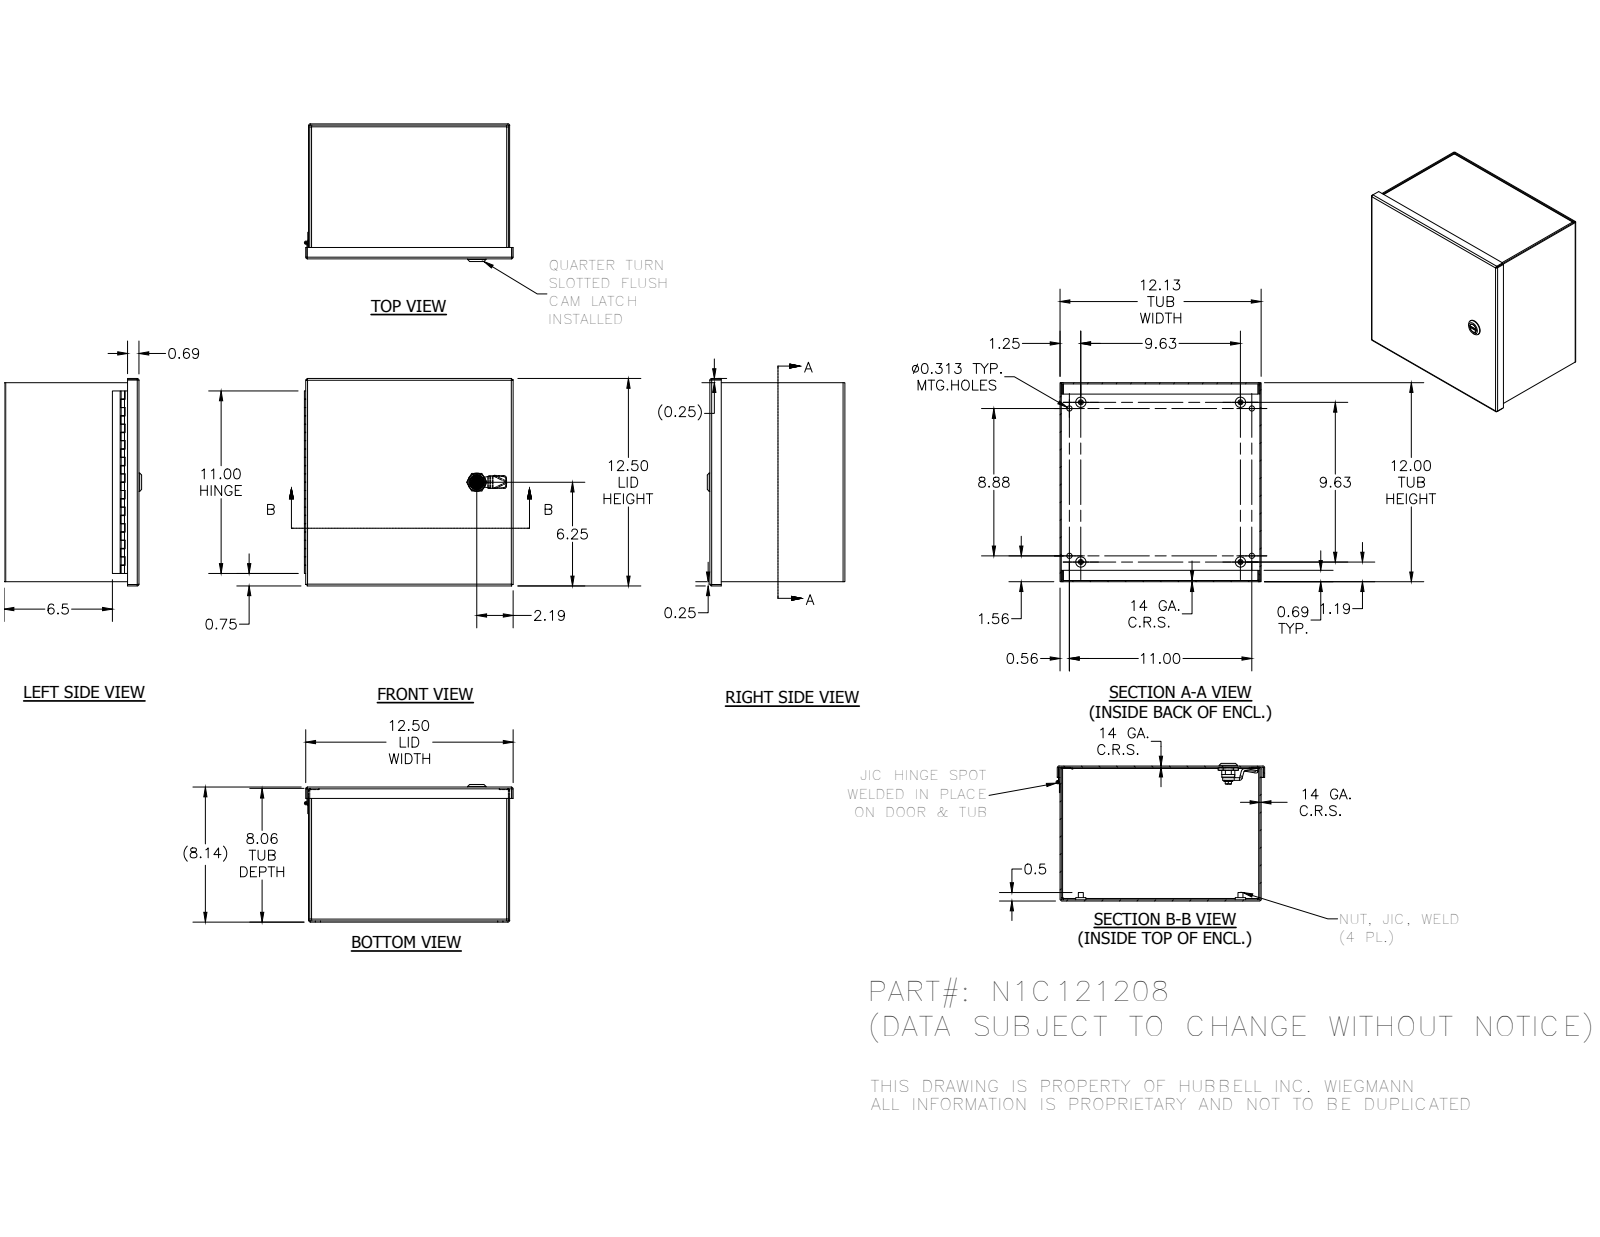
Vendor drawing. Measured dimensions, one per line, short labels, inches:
name: N1C_SMALL; N1C1208TB; N1C121208BLR; HFW3513 (+8 more)
written by: Autodesk Inventor 2012 (AUTOMOTIVE_DESIGN)
unit: in
bodies: 19 solids, 715 faces (411 planar, 222 cylindrical, 82 other)
size: 12.584 × 12.5 × 8.294
volume: 58.83 in³; area: 1 622 in²
holes: 4× ⌀0.156, 4× ⌀0.313, 1× ⌀0.116, 1× ⌀0.197, 1× ⌀0.315, 1× ⌀0.394, 1× ⌀0.402, 1× ⌀0.634, 1× ⌀0.802
bosses: 4× ⌀0.625, 4× ⌀0.3, 1× ⌀1.102, 1× ⌀0.866, 1× ⌀0.78, 1× ⌀0.63, 1× ⌀0.598, 1× ⌀0.531
rounds: 30× R0.012, 16× R0.031, 16× R0.105, 10× R0.02, 4× R0.157, 3× R0.016, 1× R0.039, 1× R0.173
face distances: 0.074, 8.063, 7.989, 12.051, 11.926, 8.137, 11.977, 12.125, 12, 11.852
hole spacings: 0.783, 9.276, 9.625, 10.319, 13.853, 4.658, 4.868, 8.875
